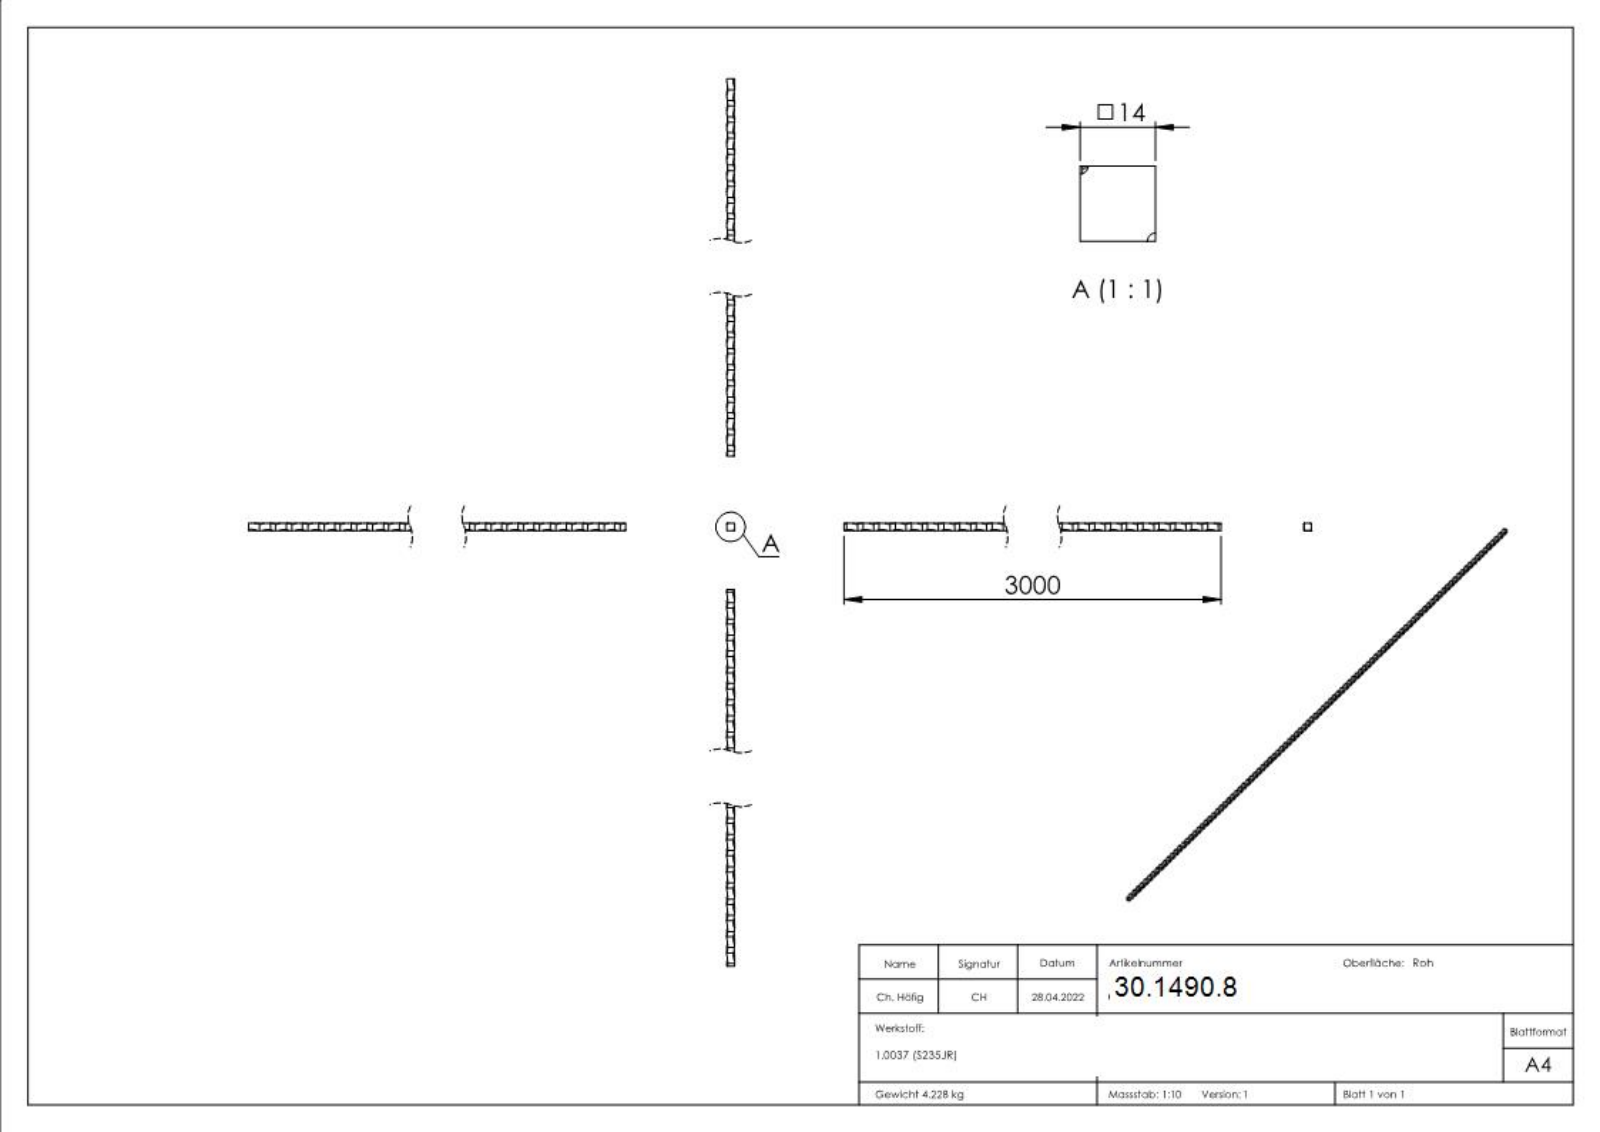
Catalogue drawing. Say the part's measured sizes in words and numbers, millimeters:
The part is named "6003". Its 3-D file was written by "SolidWorks 2018 (CONFIG_CONTROL_DESIGN)". It is 1 solid with 1405 faces: 488 planar, 406 cylindrical and 511 other. Overall it measures 3000 by 14 by 14 millimeters. Its volume is 542 042 cubic millimeters and its surface area 159 310 square millimeters. Partial cylindrical surfaces (rounded edges, fillets, slot ends): 400 of radius 100.25. The main face-to-face distances are 14, 3000, 0.5, 13.5, 1504.85, 1495.15, 8.2, 5.8, 7.95, 6.05.
